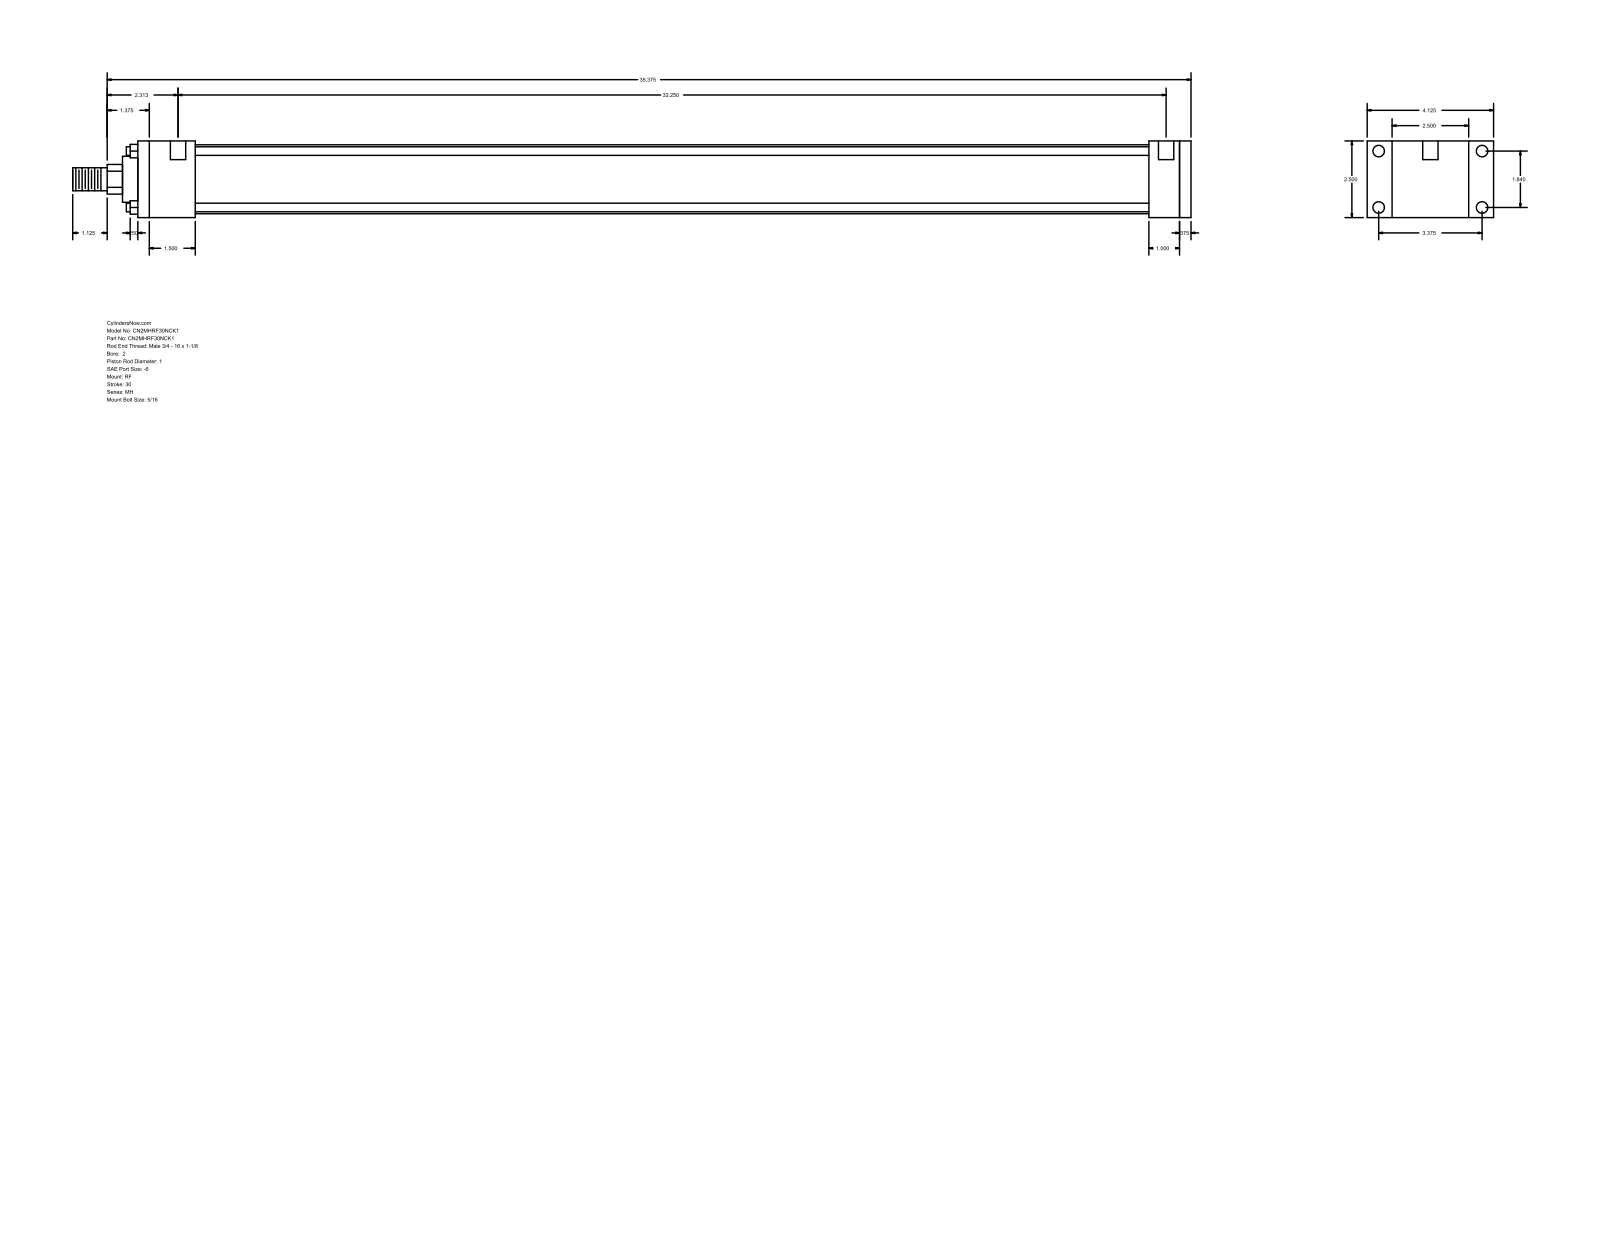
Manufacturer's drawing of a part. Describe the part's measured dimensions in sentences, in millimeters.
The part is named "MH_RF__0200_1". Its 3-D file was written by "GSSL Pune (CONFIG_CONTROL_DESIGN)". It is 0 solids with 92 faces: 64 planar, 28 cylindrical and 0 other. Overall it measures 927.1 by 104.78 by 63.5 millimeters. Round holes: 4 of diameter 5.56, 4 of diameter 9.53, 2 of diameter 12.7. Round bosses or shafts: 4 of diameter 7.14, 1 of diameter 57.15, 1 of diameter 38.1, 1 of diameter 25.4, 1 of diameter 19.05. Partial cylindrical surfaces (rounded edges, fillets, slot ends): 1 of radius 12.29. The main face-to-face distances are 63.5, 873.12, 9.52, 863.6, 20.64, 25.4, 47.63, 838.2, 790.57, 815.97. The hole center spacings are 46.74, 85.72, 97.63, 827.08, 3.17, 4.76, 819.15, 822.32.
